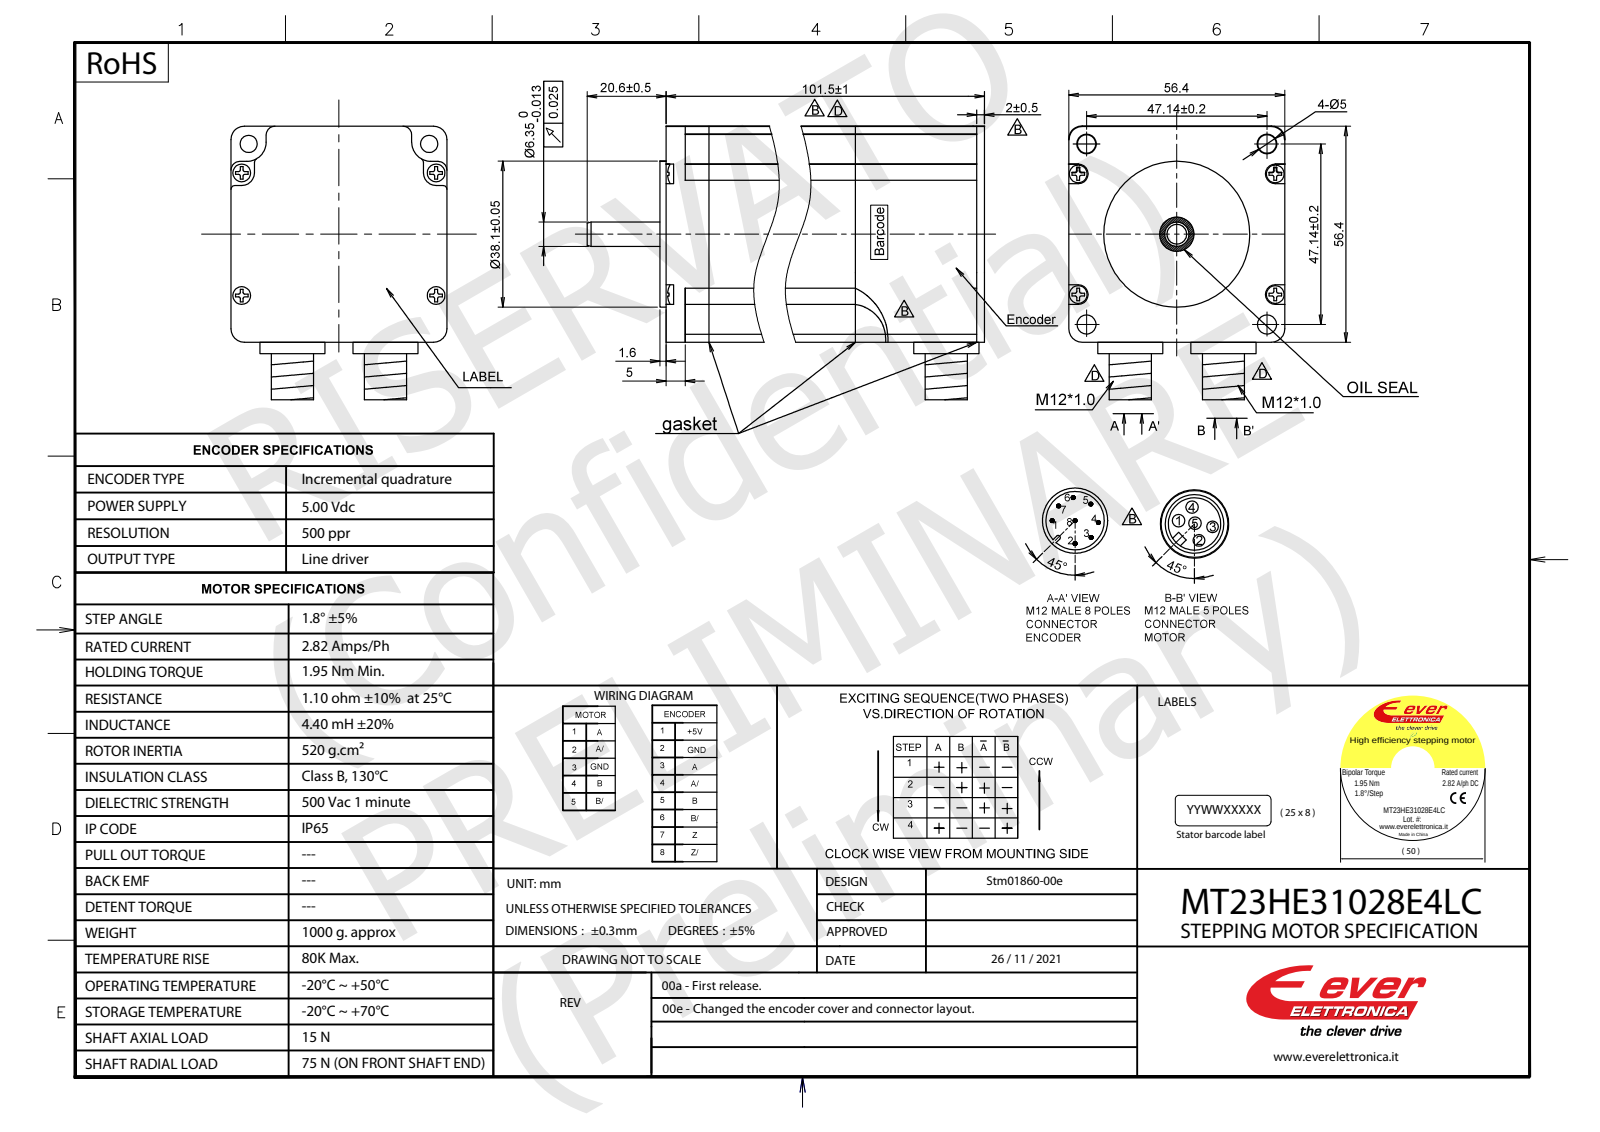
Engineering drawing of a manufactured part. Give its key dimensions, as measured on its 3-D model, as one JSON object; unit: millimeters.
{"part_name": "NEMA23STATOR_3_1_2_1_1_1; MT23HE22028E4LVFRONTENDBELL_6_1; MT23HE22028E4LV_ASM_3_1_ASM_1_A_ASM; PRT0012_1_1_1 (+8 more)", "step_written_by": "CREO PARAMETRIC BY PTC INC, 2017260 (CONFIG_CONTROL_DESIGN)", "units": "millimeters", "bodies": {"solids": 7, "faces": 2147, "planar": 691, "cylindrical": 643, "other": 813}, "overall_size": [121.1, 75.73, 56.87], "volume_mm3": 138408, "surface_area_mm2": 88090, "round_holes": [[2.5, 11], [1, 5], [3.3, 4], [5, 4], [1.2, 2], [9.6, 2], [6.35, 1], [11, 1], [22, 1]], "round_bosses_or_shafts": [[1.5, 13], [0.8, 8], [1.45, 5], [14.38, 2], [13.5, 2], [10.92, 2], [10.6, 2], [9.5, 2]], "partial_cylinders_radius": [[1, 42], [0.5, 41], [0.3, 28], [2.3, 27], [2, 20], [3.5, 20], [5, 13], [0.6, 10]], "face_to_face_distances": [3, 56.2, 22.4, 25.4, 97.5, 2.4, 100.5, 89.3, 86.3, 11.2], "hole_center_spacings": [2.5, 3.54, 7.78, 30, 33.33, 39.61, 47.14, 49.53]}
